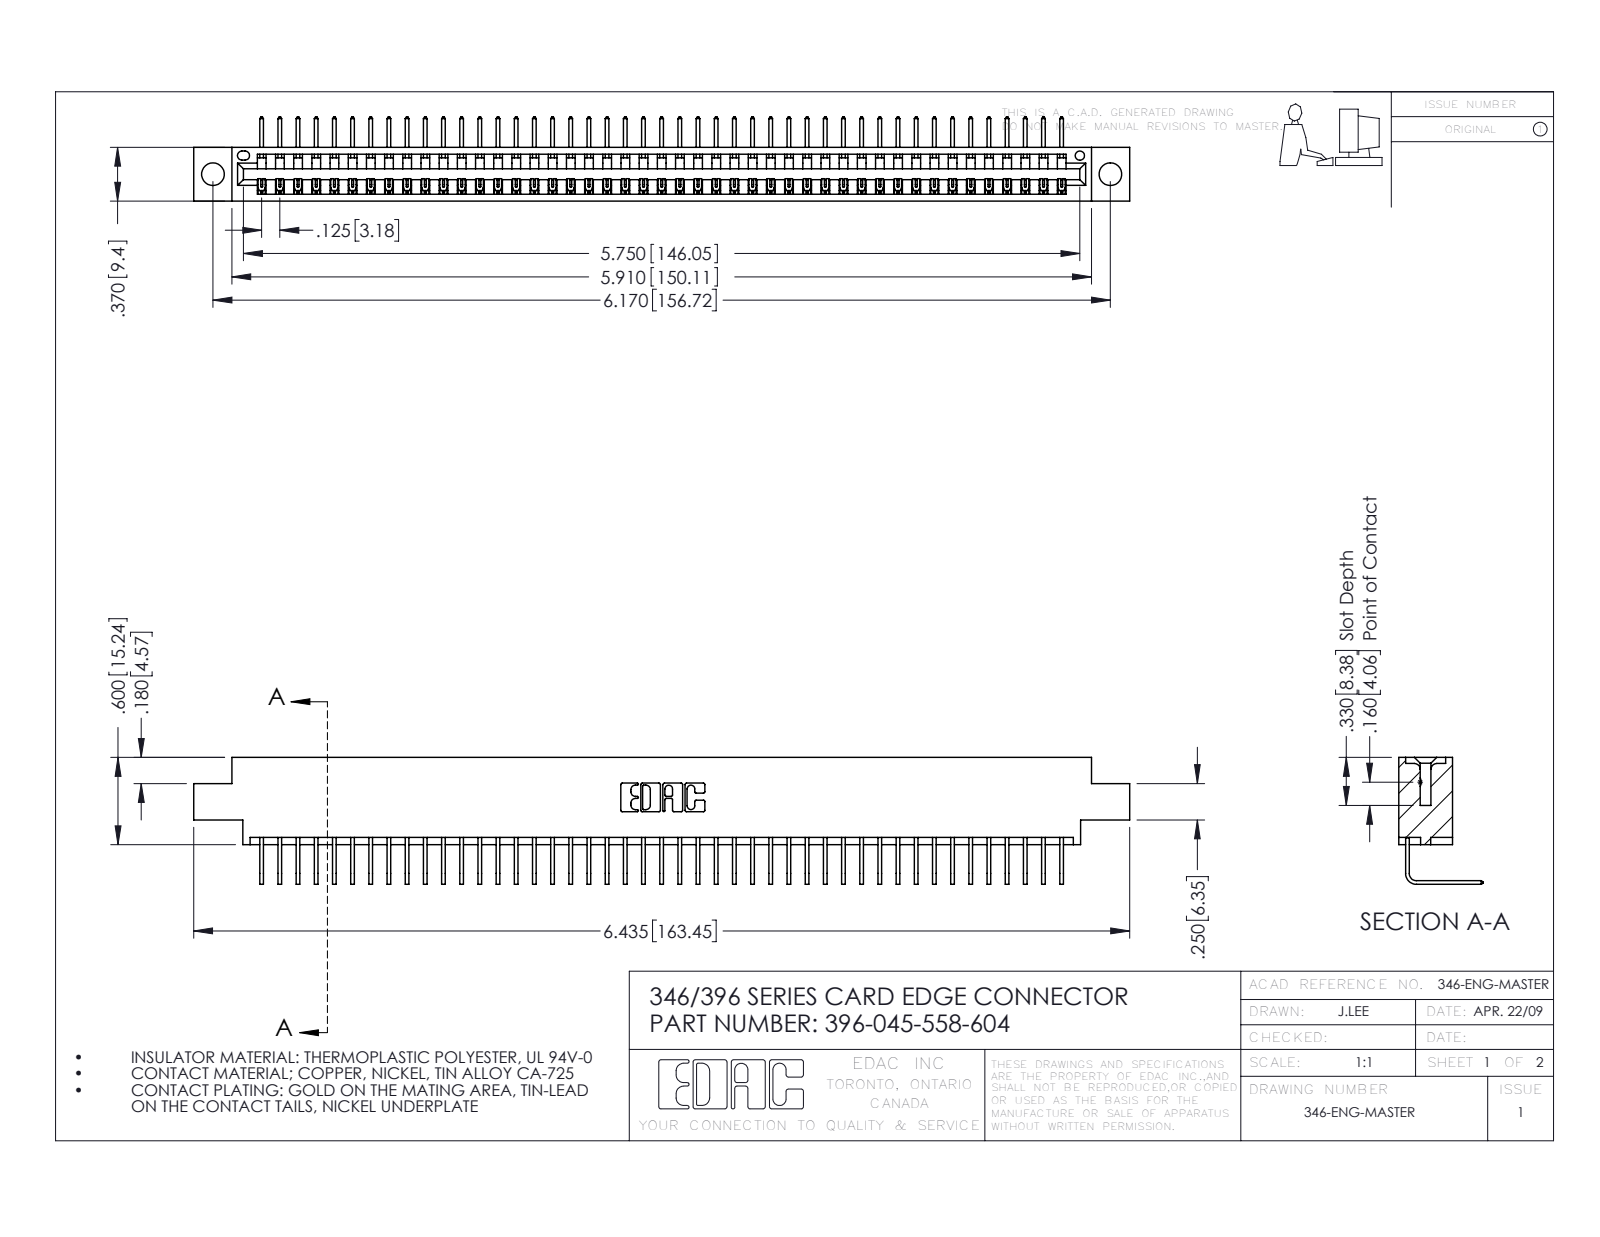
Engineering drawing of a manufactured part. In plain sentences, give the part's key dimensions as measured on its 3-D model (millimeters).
The part is named "396-045-558-604; 345-292-001_558 Tail - 2; 346 Part_0.170 Offset - 0.156 Dia-TH". Its 3-D file was written by "SolidWorks 2016 (CONFIG_CONTROL_DESIGN)". It is 46 solids with 2826 faces: 1970 planar, 856 cylindrical and 0 other. Overall it measures 163.4 by 22.2 by 14.7 millimeters. Its volume is 15 600 cubic millimeters and its surface area 20 350 square millimeters. Round holes: 2 of diameter 4, 1 of diameter 1.6. Partial cylindrical surfaces (rounded edges, fillets, slot ends): 90 of radius 0.2, 22 of radius 0.3, 6 of radius 0.2, 6 of radius 0.8, 3 of radius 0.7, 2 of radius 0.8, 2 of radius 1, 1 of radius 0.4. The main face-to-face distances are 8.2, 1.2, 9.4, 6.4, 7.6, 0.6, 1.8, 3.8, 5.6, 2.5. The hole center spacings are 6.2, 151.4, 156.7.
